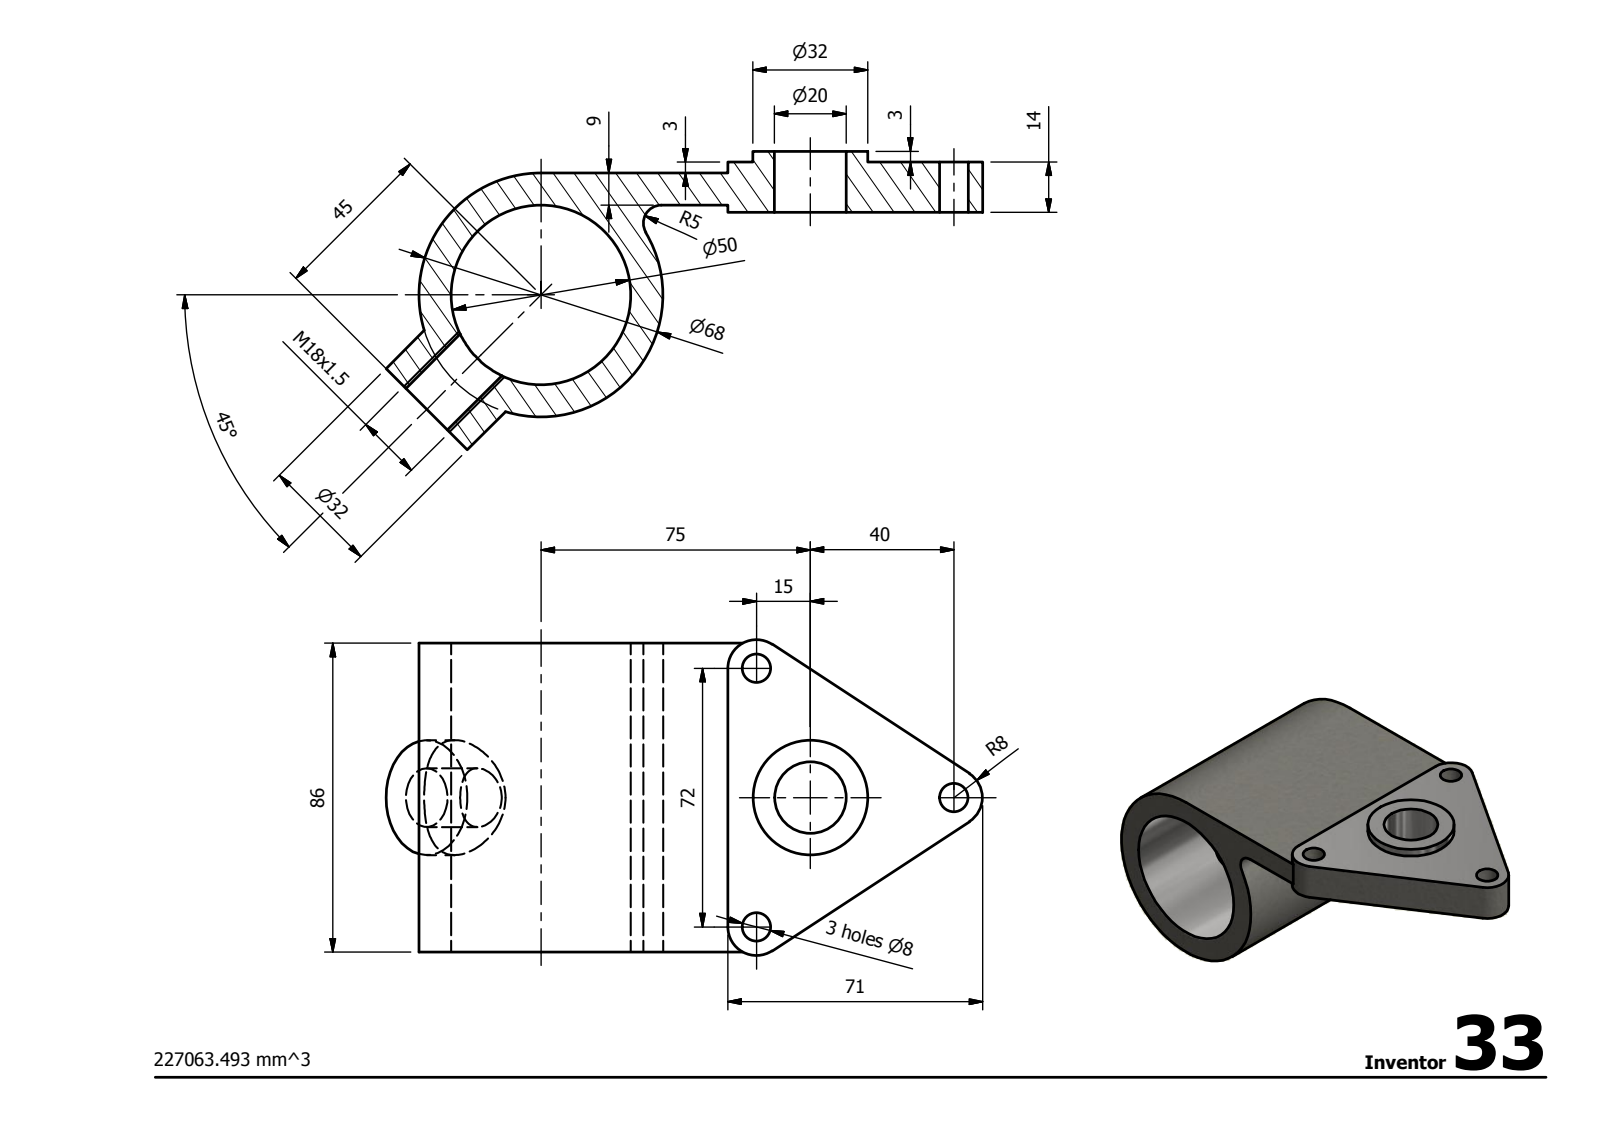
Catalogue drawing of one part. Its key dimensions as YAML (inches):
step_written_by: "Autodesk Inventor 2014 (AUTOMOTIVE_DESIGN)"
units: inches
bodies: {solids: 1, faces: 25, planar: 12, cylindrical: 13, other: 0}
overall_size: [6.541, 3.465, 3.273]
volume: 13.86
surface_area: 83.33
round_holes:
  - {diameter: 0.315, count: 3}
  - {diameter: 0.645, count: 1}
  - {diameter: 0.787, count: 1}
  - {diameter: 1.969, count: 1}
round_bosses_or_shafts:
  - {diameter: 1.26, count: 2}
  - {diameter: 2.677, count: 1}
partial_cylinders:
  - {radius: 0.315, count: 3}
  - {radius: 0.197, count: 1}
face_to_face_distances: [0.118, 0.433, 0.551, 3.386, 0.079, 0.354, 0.472, 0.669, 0.591, 0.236]
hole_center_spacings: [1.535, 2.588, 1.575, 2.835]
